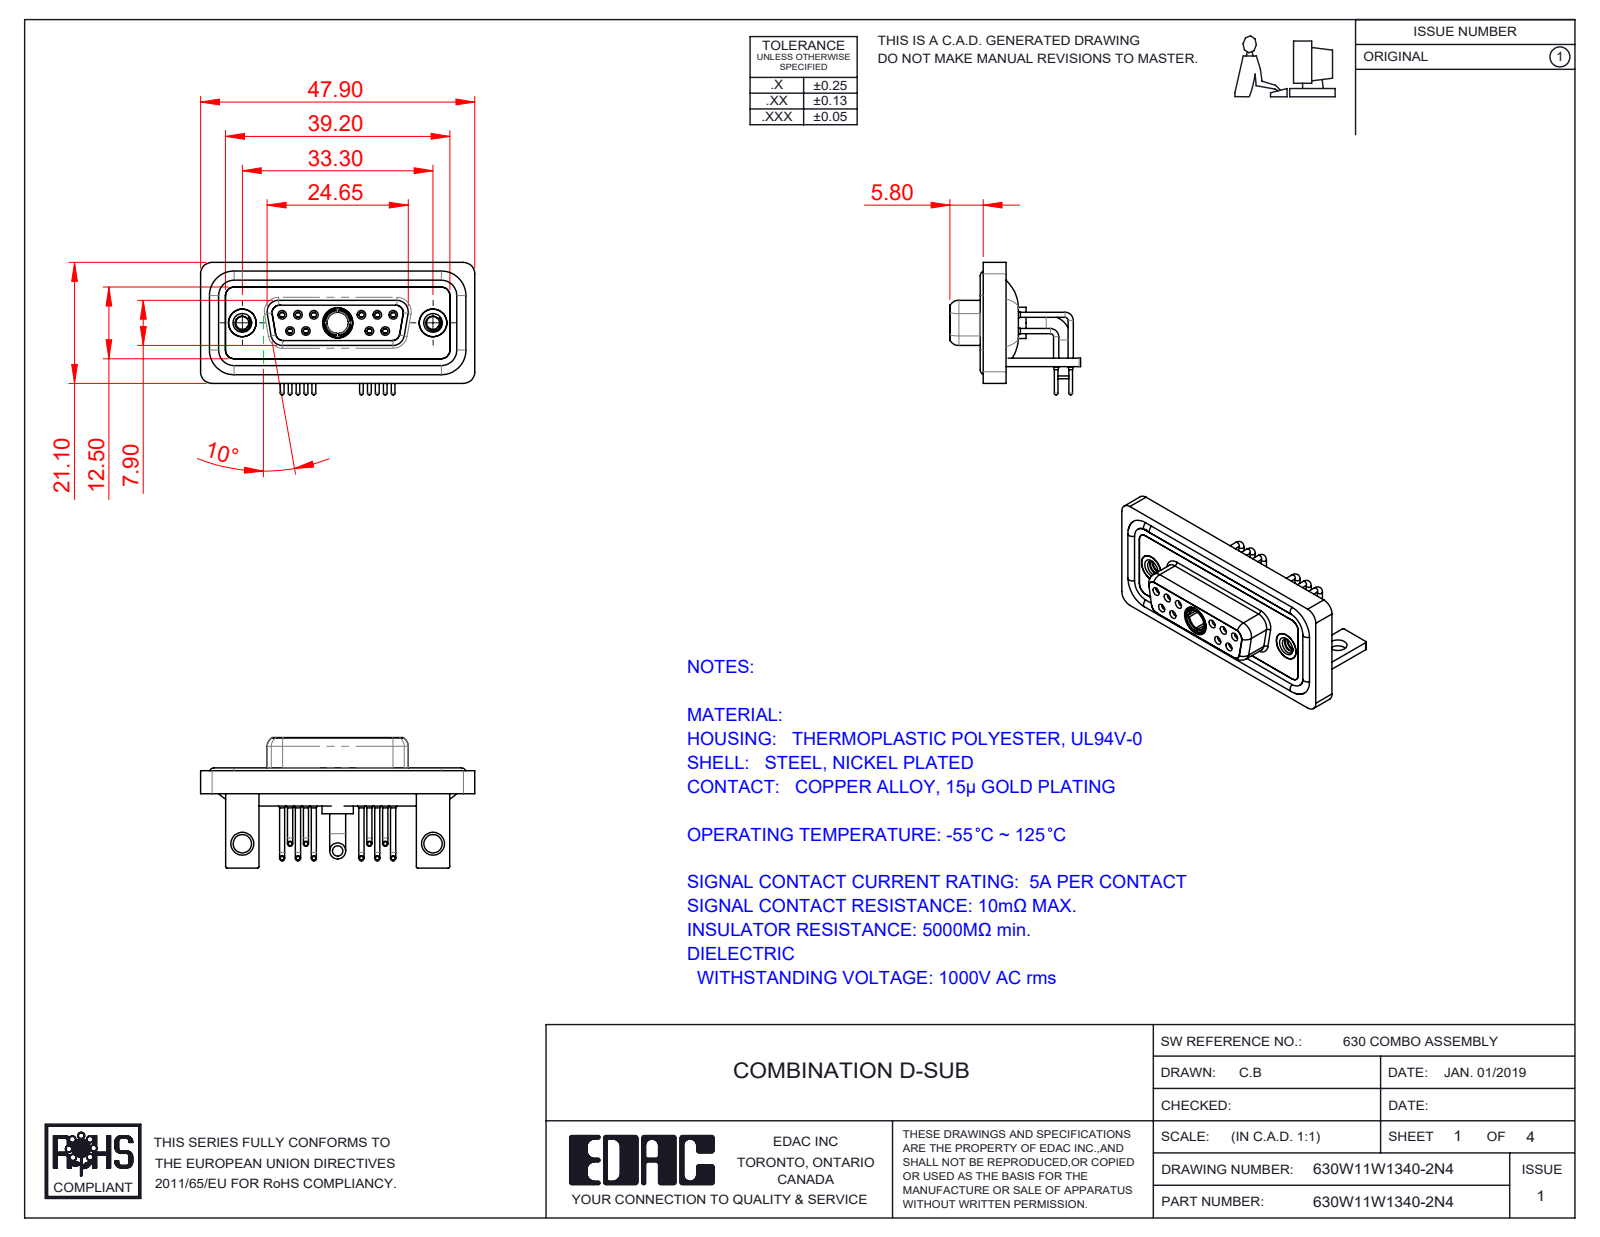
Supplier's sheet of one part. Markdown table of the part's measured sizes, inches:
| quantity | value |
| --- | --- |
| part name | 630Combo Threaded Rivet_2; 630Combo Waterproof Housing_15 Contacts; 630Combo Housing_11W1; 630W11W1340-2N4 (+6 more) |
| STEP written by | SolidWorks 2023 (CONFIG_CONTROL_DESIGN) |
| units | inches |
| bodies | 21 solids, 1042 faces (304 planar, 467 cylindrical, 271 other) |
| overall size | 1.886 × 0.91 × 0.898 |
| volume | 0.402 in³ |
| surface area | 17.37 in² |
| round holes (diameter × count) | 0.035 × 10, 0.043 × 10, 0.059 × 10, 0.079 × 10, 0.067 × 6, 0.063 × 4, 0.191 × 3, 0.089 × 2, 0.126 × 2, 0.157 × 2, 0.159 × 2, 0.197 × 2 |
| round bosses / shafts (diameter × count) | 0.063 × 10, 0.035 × 10, 0.026 × 10, 0.195 × 2, 0.189 × 2, 0.11 × 2, 0.217 × 1, 0.205 × 1 |
| partial cylindrical surfaces (radius × count) | 0.079 × 21, 0.059 × 18, 0.01 × 16, 0.053 × 12, 0.063 × 8, 0.02 × 5, 0.024 × 4, 0.026 × 4 |
| main face-to-face distances | 0.016, 0.114, 0.071, 0.059, 0.146, 0.043, 0.063, 0.161, 0.031, 0.098 |
| hole center spacings | 0.124, 0.109, 0.545, 0.436, 0.654, 0.198, 0.198, 0.218 |
